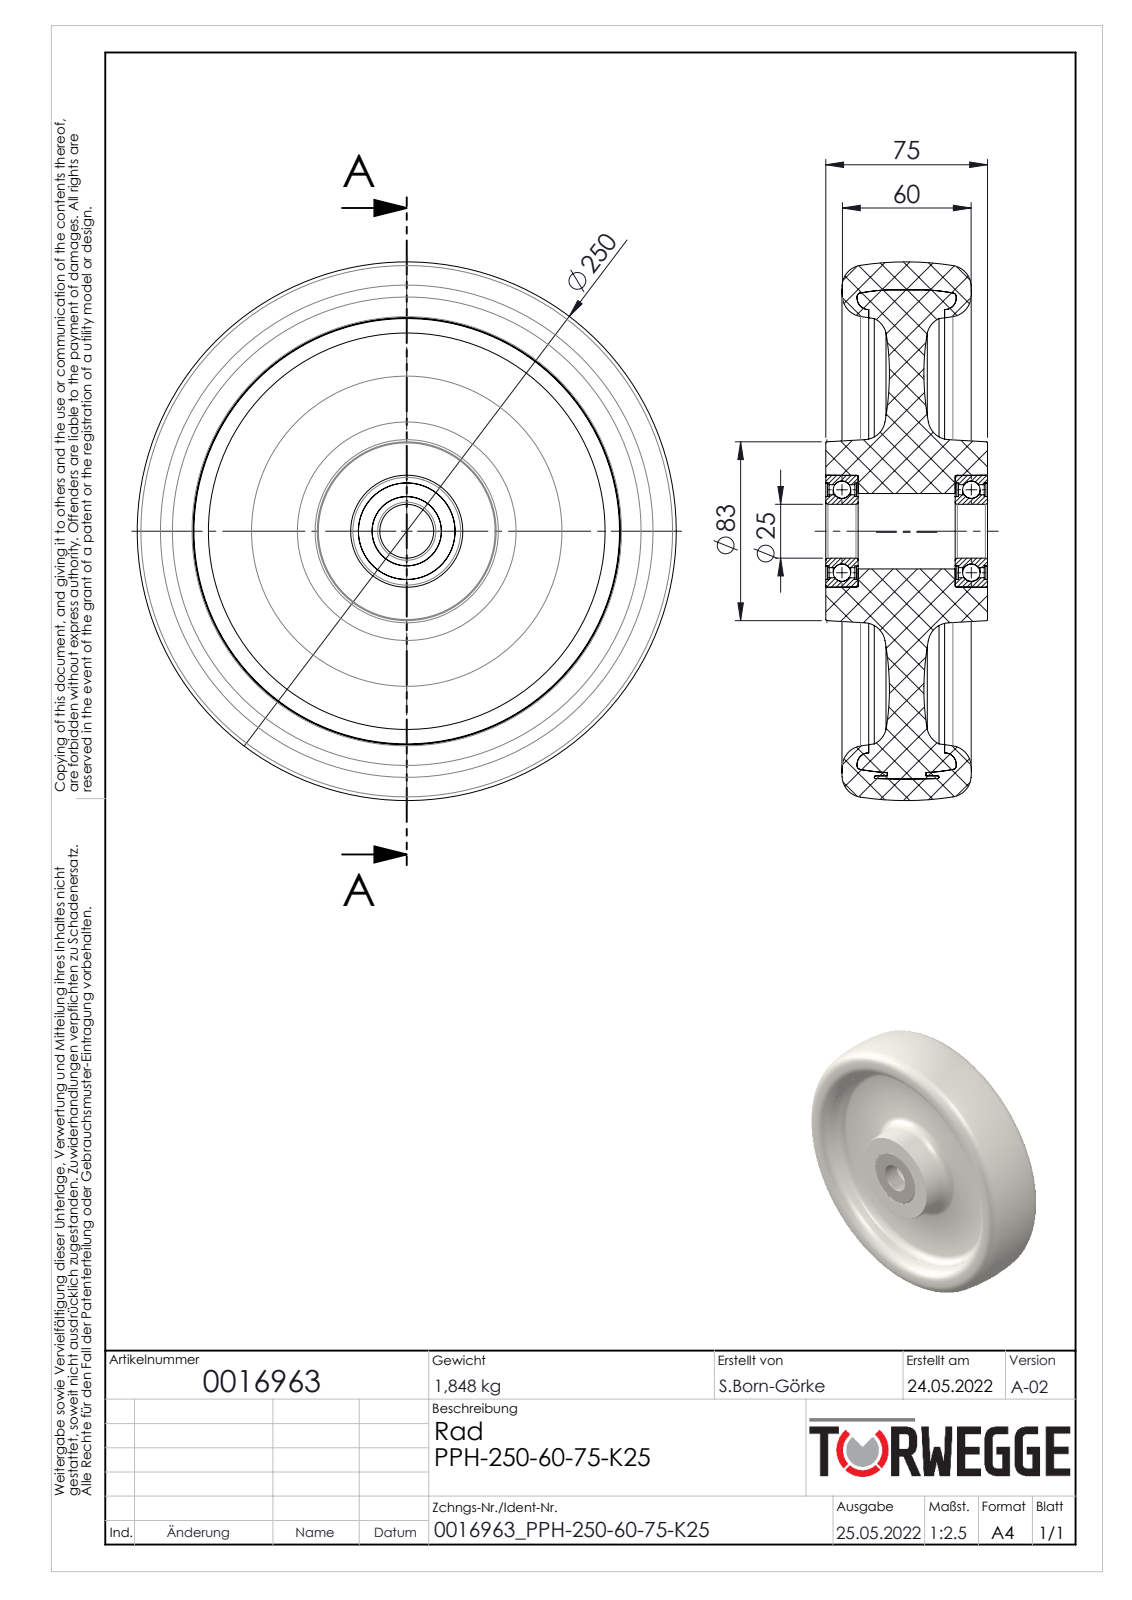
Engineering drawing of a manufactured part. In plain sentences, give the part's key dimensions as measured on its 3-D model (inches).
The part is named "0016963". Its 3-D file was written by "SolidWorks 2020 (AUTOMOTIVE_DESIGN)". It is 12 solids with 344 faces: 84 planar, 98 cylindrical and 162 other. Overall it measures 9.843 by 9.843 by 2.953 inches. Its volume is 111.1 cubic inches and its surface area 526.9 square inches. Round holes: 1 of diameter 0.984, 1 of diameter 1.266, 1 of diameter 1.378, 1 of diameter 1.701, 1 of diameter 1.765, 1 of diameter 8.937. Round bosses or shafts: 1 of diameter 2.047, 1 of diameter 1.766, 1 of diameter 1.331, 1 of diameter 1.266. Partial cylindrical surfaces (rounded edges, fillets, slot ends): 6 of radius 4.409. The main face-to-face distances are 0.783, 2.169, 2.362, 0.591, 0.193, 1.579, 1.386, 2.953, 0.03, 1.122.
